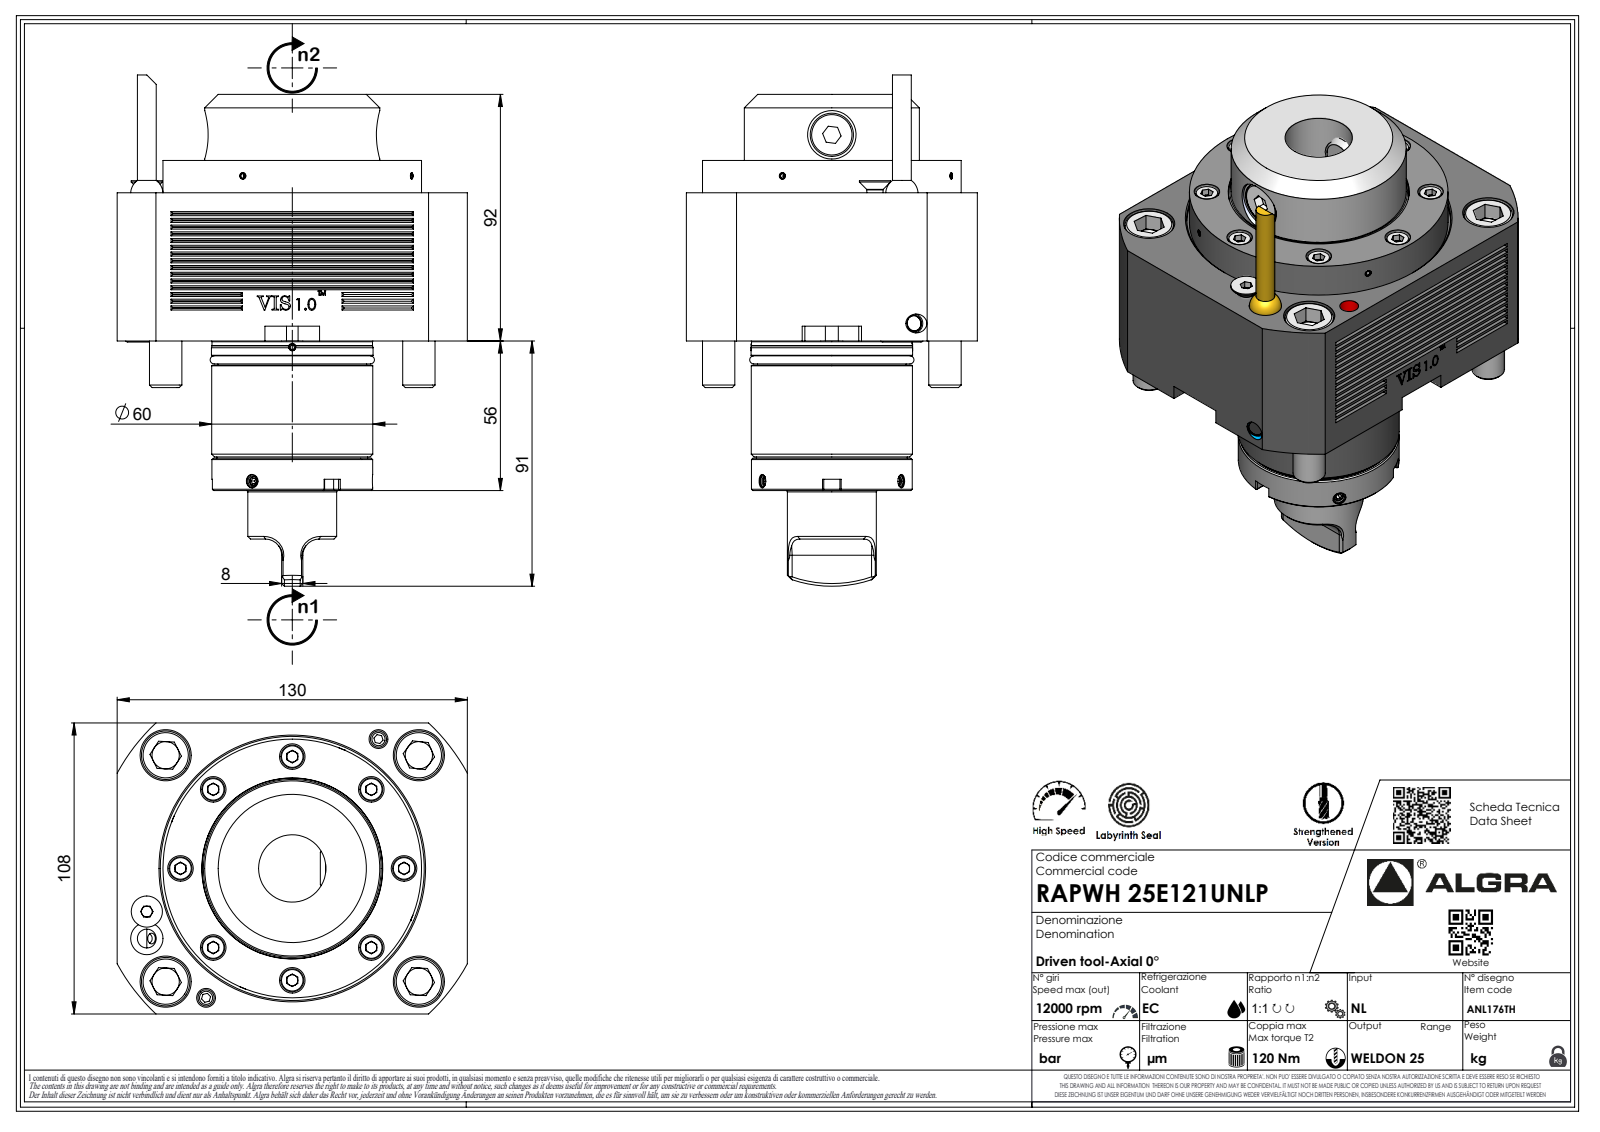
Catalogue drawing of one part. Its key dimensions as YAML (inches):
part_name: "RAPWH25E121UNLP"
step_written_by: "SolidWorks 2023 (AUTOMOTIVE_DESIGN)"
units: inches
bodies: {solids: 1, faces: 417, planar: 278, cylindrical: 58, other: 81}
overall_size: [7.469, 5.118, 4.252]
volume: 66.45
surface_area: 119.4
round_holes:
  - {diameter: 0.083, count: 1}
  - {diameter: 0.157, count: 1}
round_bosses_or_shafts:
  - {diameter: 0.472, count: 4}
  - {diameter: 3.78, count: 1}
  - {diameter: 2.559, count: 1}
  - {diameter: 2.362, count: 1}
  - {diameter: 2.346, count: 1}
  - {diameter: 1.299, count: 1}
  - {diameter: 0.276, count: 1}
  - {diameter: 0.251, count: 1}
partial_cylinders:
  - {radius: 0.315, count: 8}
  - {radius: 0.013, count: 7}
  - {radius: 0.02, count: 7}
  - {radius: 0.146, count: 7}
  - {radius: 0.236, count: 6}
  - {radius: 0.008, count: 1}
  - {radius: 0.079, count: 1}
  - {radius: 1.811, count: 1}
face_to_face_distances: [2.165, 4.252, 2.638, 0.472, 5.118, 3.602, 1.437, 0.965, 2.185, 4.35]
